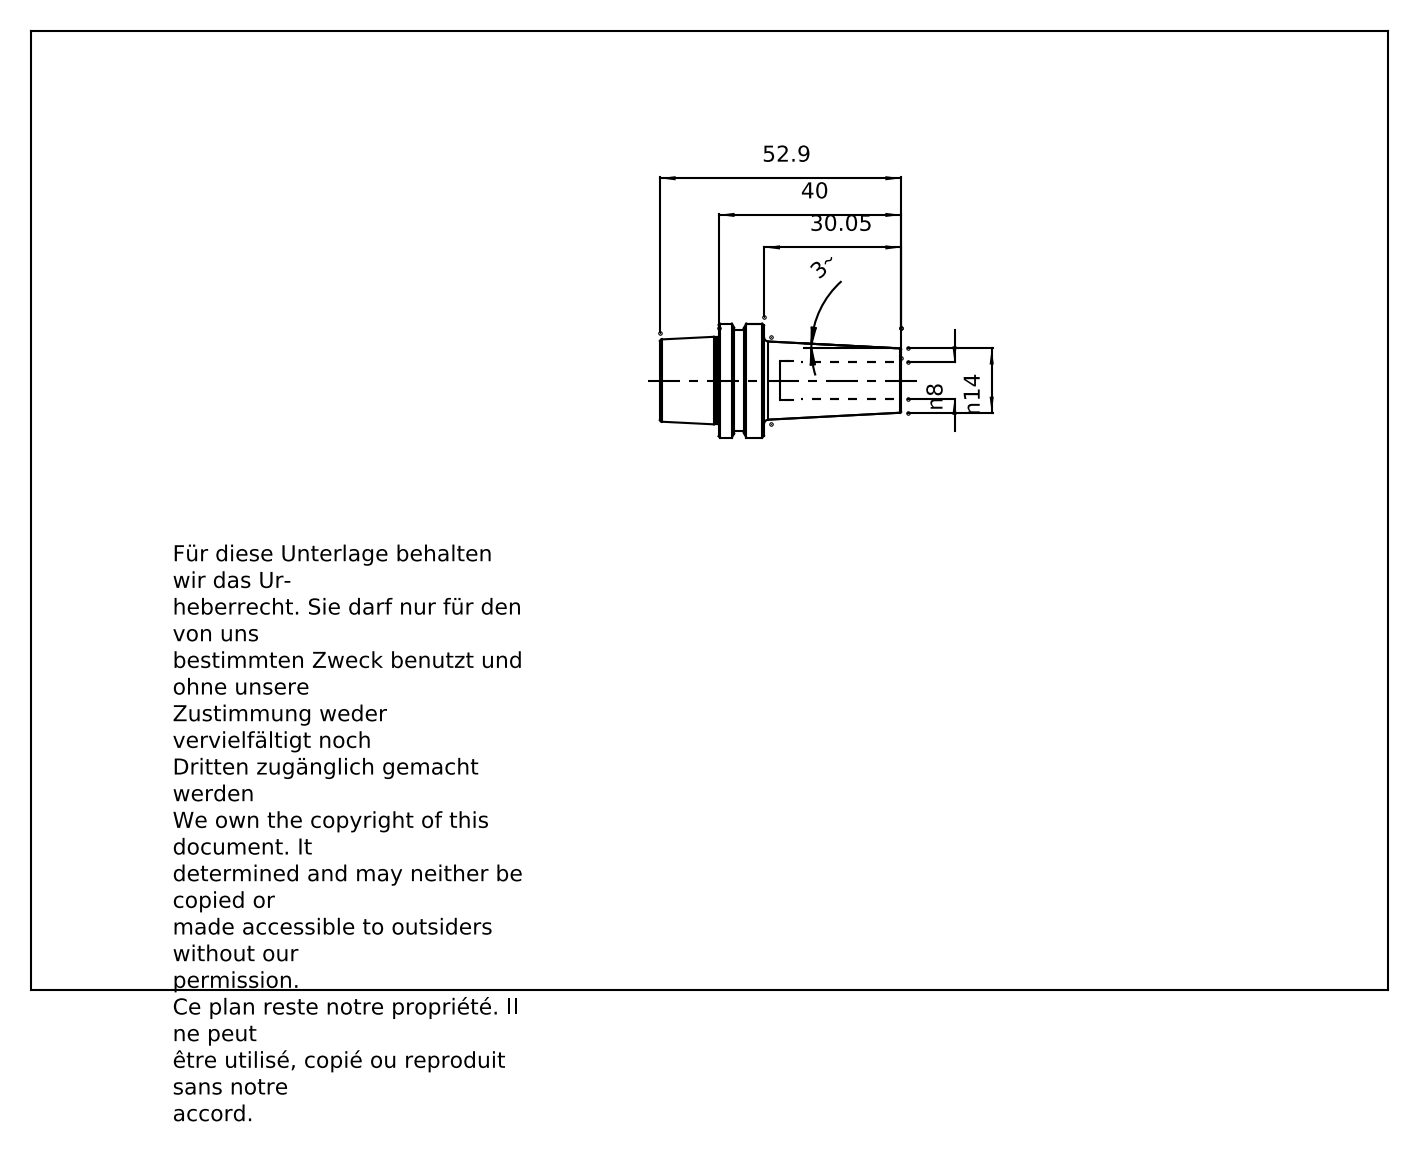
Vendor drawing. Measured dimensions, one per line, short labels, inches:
name: E25-185-08
written by: PRO/ENGINEER BY PARAMETRIC TECHNOLOGY CORPORATION, 2010430 (CONFIG_CONTROL_DESIGN)
unit: in
bodies: 1 solid, 60 faces (8 planar, 16 cylindrical, 36 other)
size: 2.083 × 0.984 × 0.984
volume: 0.561 in³; area: 8.644 in²
holes: 1× ⌀0.315, 1× ⌀0.553, 1× ⌀0.648
bosses: 1× ⌀0.984, 1× ⌀0.864, 1× ⌀0.746
face distances: 0.157, 0.234, 0.392, 1.575, 1.341, 1.183, 0.508, 0.742, 0.9, 2.083
